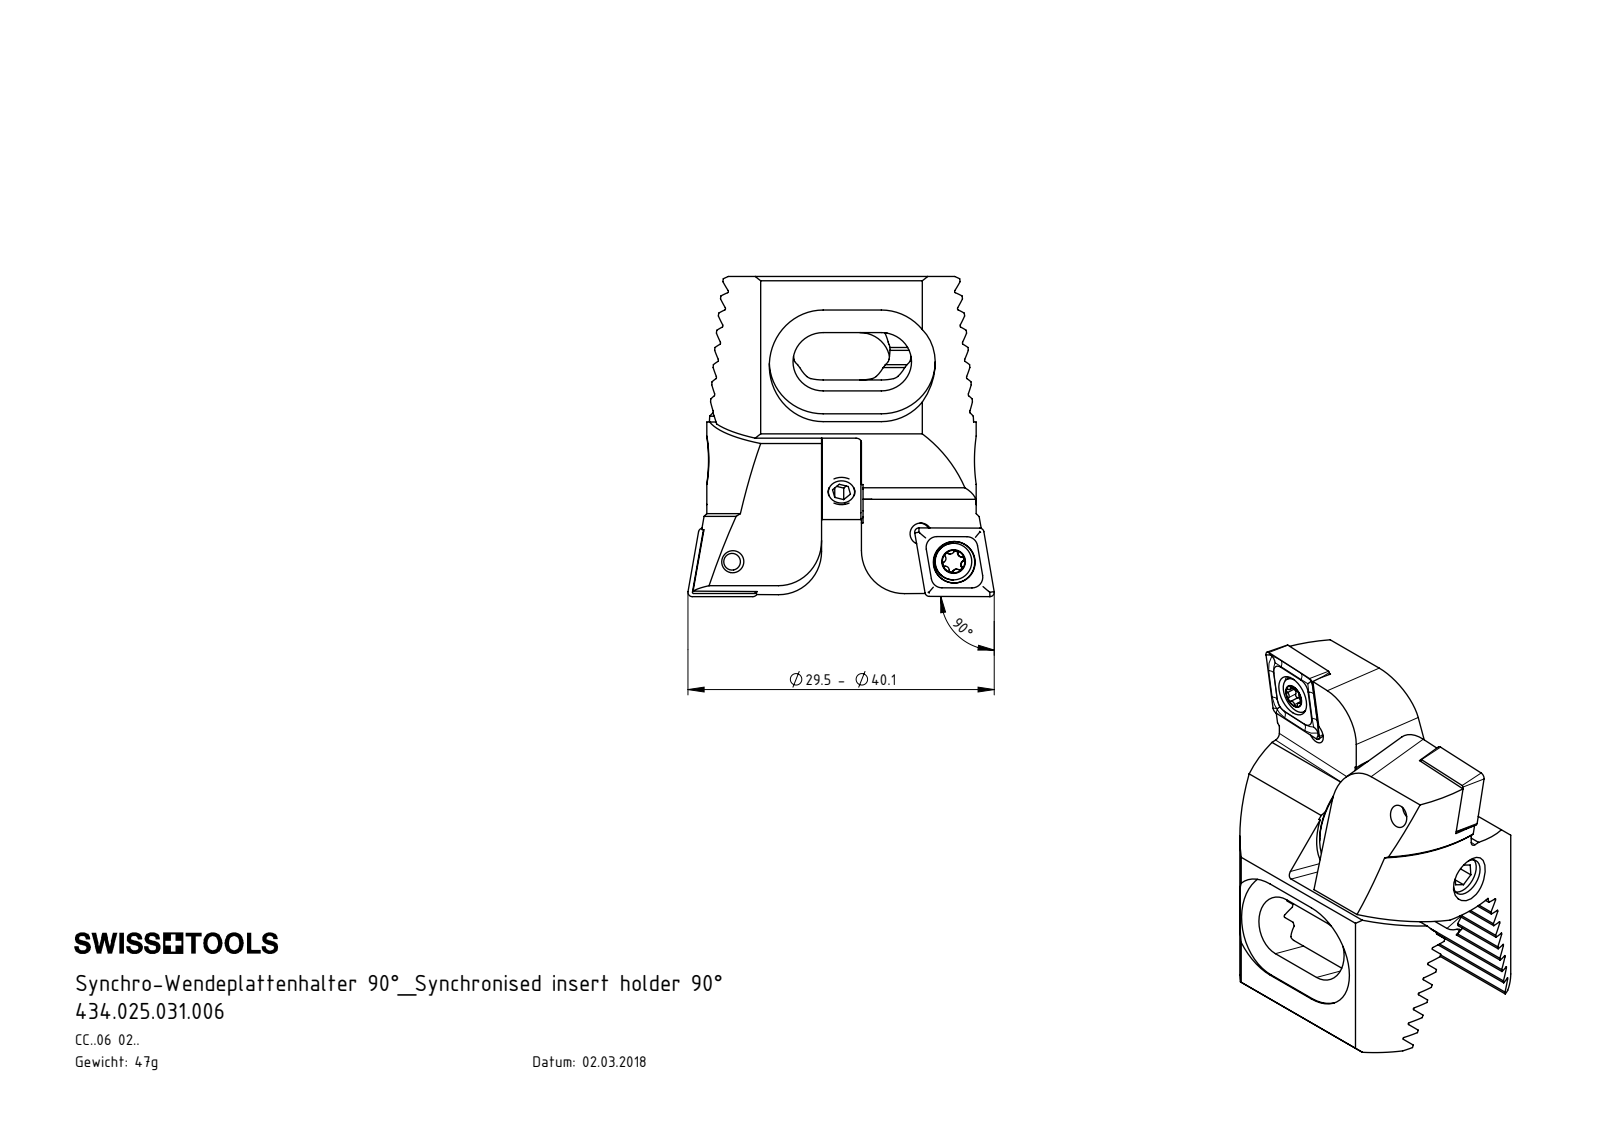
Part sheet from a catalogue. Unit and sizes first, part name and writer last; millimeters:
Units: millimetres
Overall size (bounding box): 29.7 × 28.43 × 20.2
Round holes (diameter × count): ⌀1 ×3, ⌀2.5 ×3, ⌀2 ×2, ⌀2.05 ×2, ⌀2.8 ×2, ⌀3.85 ×2, ⌀3.5 ×1
Round bosses / shafts (diameter × count): ⌀3 ×4, ⌀3.4 ×2, ⌀2.5 ×2, ⌀11 ×1, ⌀4 ×1
Partial cylindrical surfaces — rounded edges, fillets, slot ends (radius × count): R0.12 ×16, R0.21 ×12, R0.36 ×10, R1 ×8, R0.5 ×4, R2.8 ×4, R5 ×4, R0.36 ×2
Main face-to-face distances: 1.43, 2.86, 4.29, 5.72, 3.14, 7.14, 8.57, 7.15, 4, 5.71
Hole centre spacings: 2, 3.98, 3.99, 4.08, 4.09, 7.19, 7.2, 7.47
Volume: 5 848 mm³ · Surface area: 5 400 mm²
Bodies: 11 solids, 517 faces (205 planar, 172 cylindrical, 140 other)
Part name (STEP PRODUCT): 434.025.031.006; Z25-ER3.002.004_B; Z25-ER3.001.023_A; CCMT060204 (+4 more)
STEP written by: SolidWorks 2017 (CONFIG_CONTROL_DESIGN)
